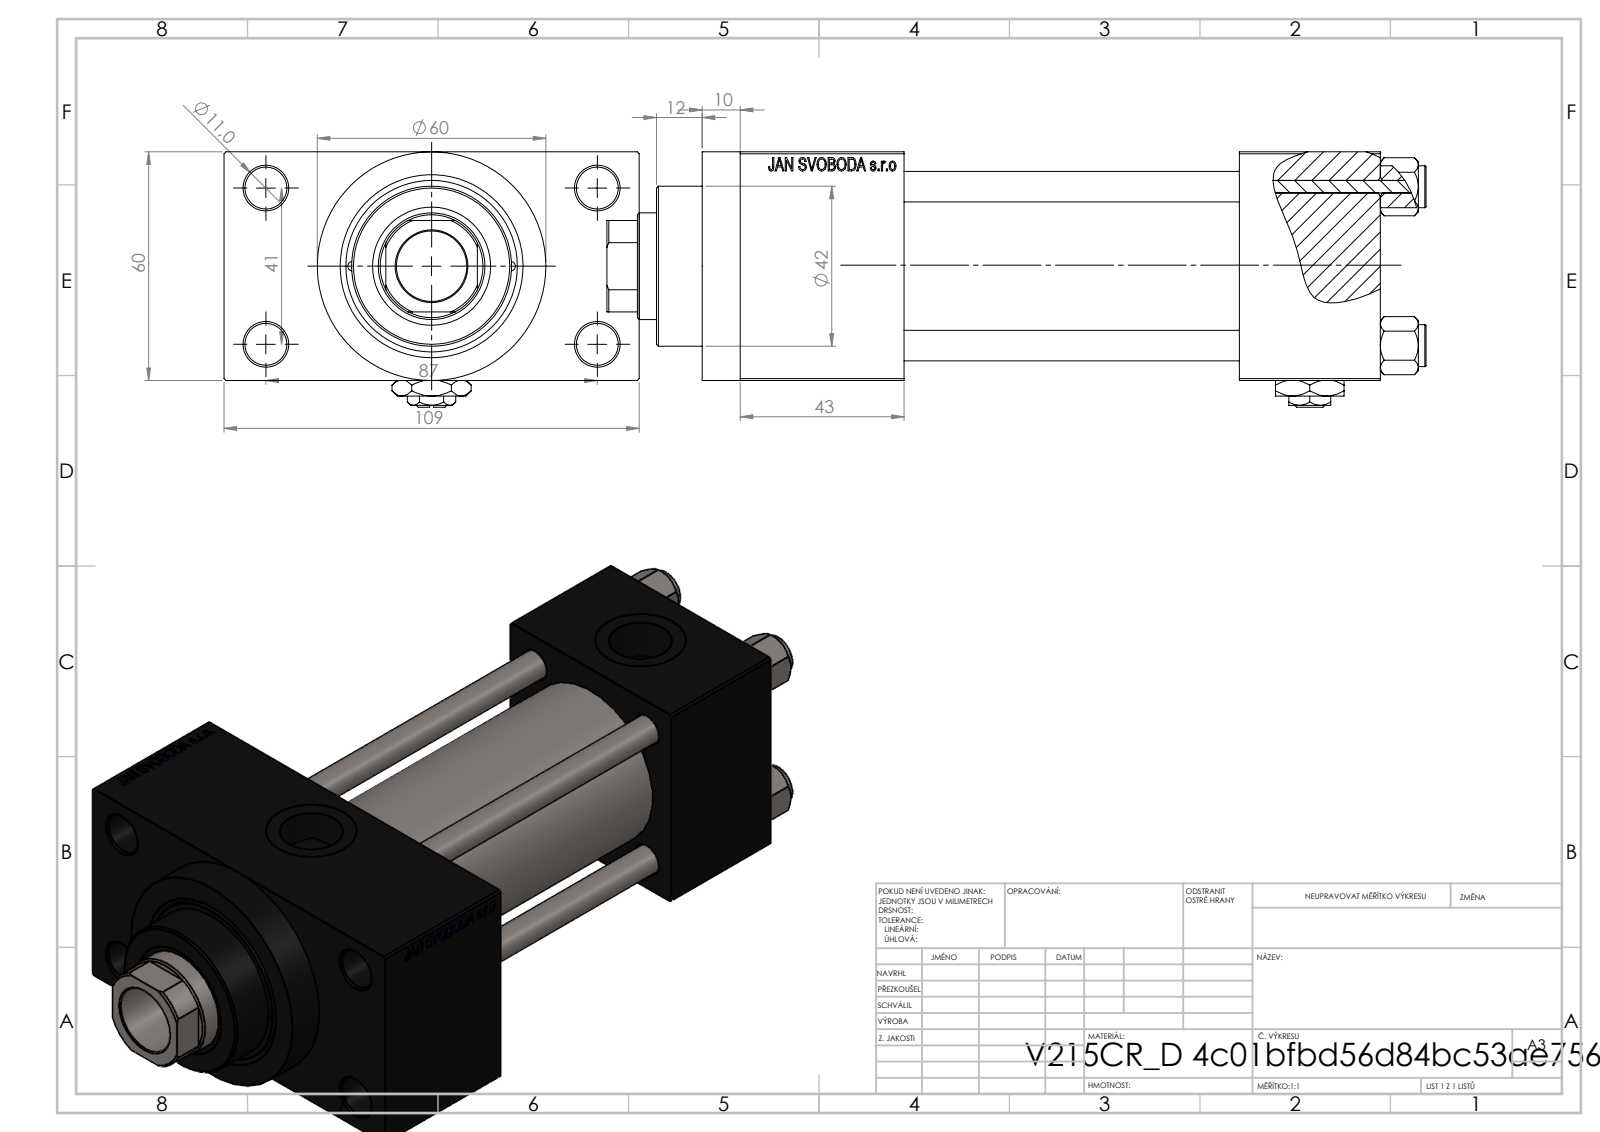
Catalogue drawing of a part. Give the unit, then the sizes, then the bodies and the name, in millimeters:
Units: millimetres
Overall size (bounding box): 215 × 109 × 67
Round holes (diameter × count): ⌀8 ×4, ⌀11 ×4, ⌀2.5 ×2, ⌀7 ×2, ⌀16.66 ×2, ⌀24 ×2, ⌀18.5 ×1, ⌀28 ×1, ⌀31 ×1, ⌀40 ×1, ⌀45 ×1
Round bosses / shafts (diameter × count): ⌀11 ×4, ⌀60 ×1, ⌀46 ×1, ⌀42 ×1
Partial cylindrical surfaces — rounded edges, fillets, slot ends (radius × count): R13.5 ×1
Main face-to-face distances: 60, 24.5, 84.5, 88, 37, 125, 168, 131, 43, 109
Hole centre spacings: 20.85, 22.65, 29.49, 30.62, 41.7, 46.53, 47.15, 48.09
Volume: 568 831 mm³ · Surface area: 143 293 mm²
Bodies: 12 solids, 1168 faces (526 planar, 100 cylindrical, 542 other)
Part name (STEP PRODUCT): V215CR_VCP_D; Zatka_pro_OIL_PORT; V215CR_D_TYCINKA; V215CR_D_Body (+2 more)
STEP written by: SolidWorks 2019 (CONFIG_CONTROL_DESIGN)
